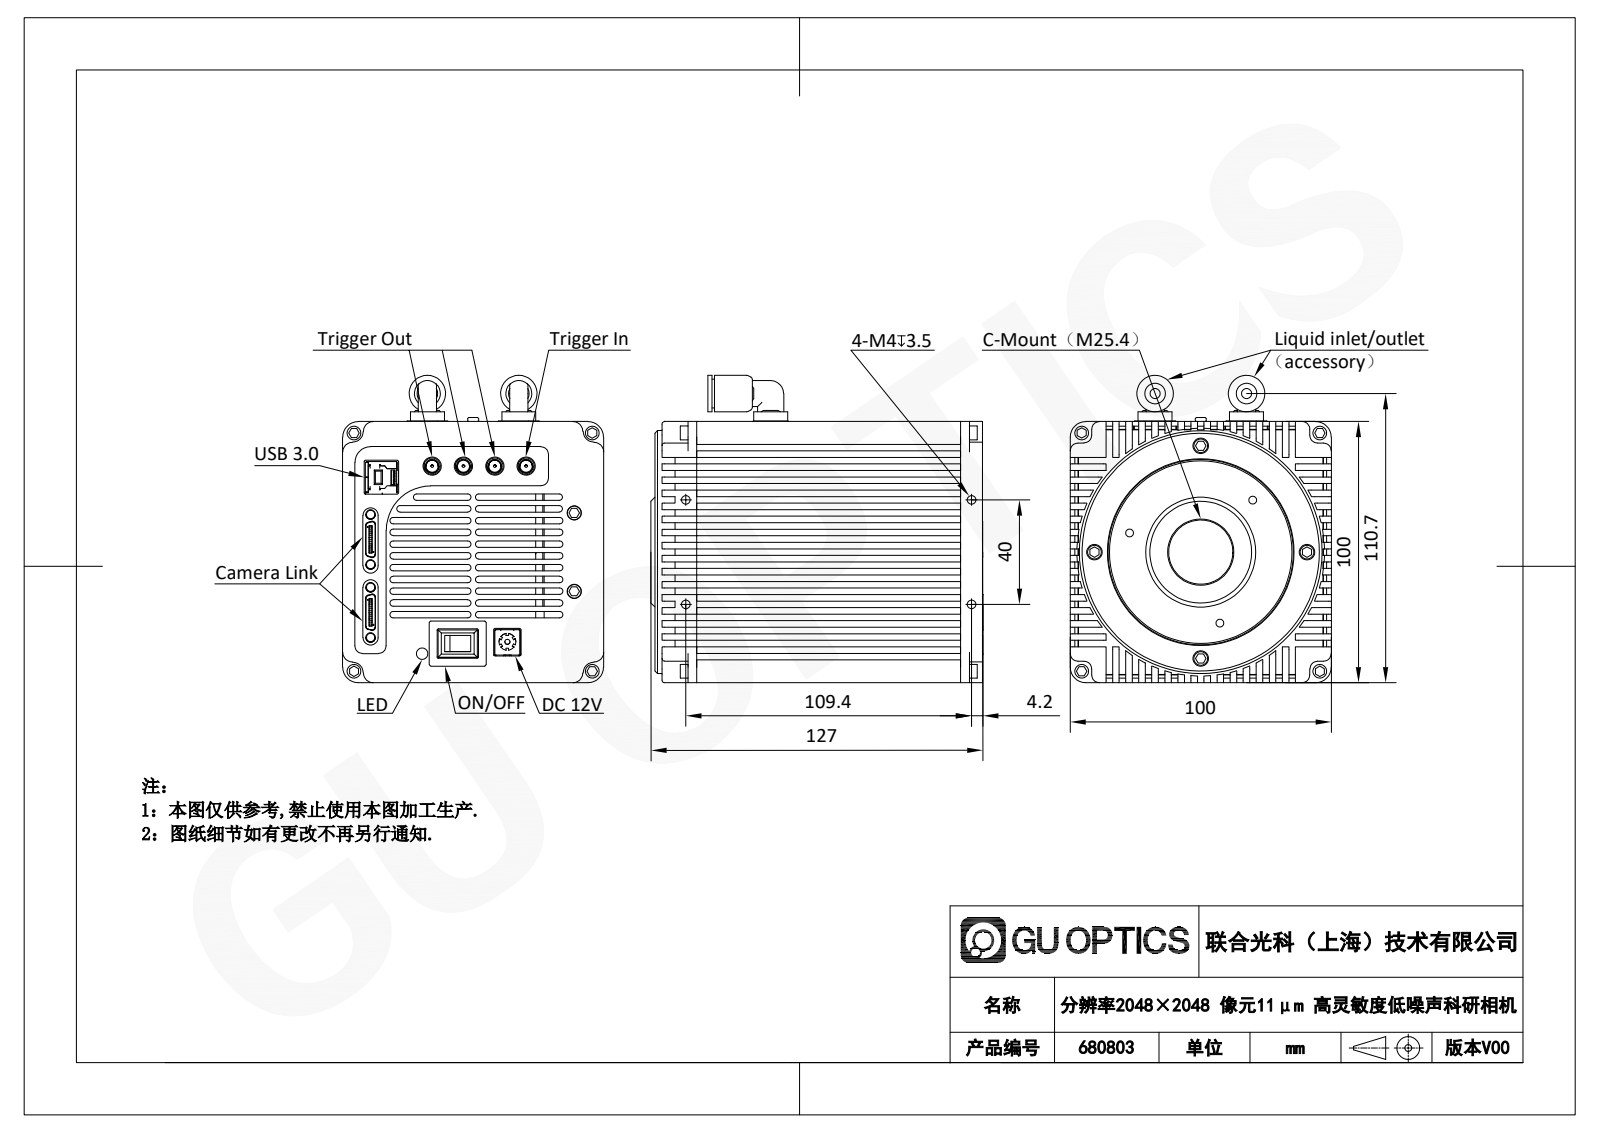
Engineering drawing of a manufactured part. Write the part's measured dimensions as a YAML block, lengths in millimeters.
part_name: "68080358.stp; 68080343.stp; 68080348.stp; 68080337.stp (+8 more)"
step_written_by: "SolidWorks 2024 (CONFIG_CONTROL_DESIGN)"
units: millimeters
bodies: {solids: 64, faces: 5520, planar: 3348, cylindrical: 1705, other: 467}
overall_size: [177.38, 117.7, 100]
volume: 1003000
surface_area: 252717
round_holes:
  - {diameter: 3.2, count: 18}
  - {diameter: 6, count: 12}
  - {diameter: 2.2, count: 10}
  - {diameter: 2.6, count: 10}
  - {diameter: 1.6, count: 6}
  - {diameter: 2, count: 5}
  - {diameter: 1, count: 4}
  - {diameter: 2.5, count: 4}
  - {diameter: 3.4, count: 4}
  - {diameter: 4.3, count: 4}
  - {diameter: 4.65, count: 4}
  - {diameter: 7, count: 4}
round_bosses_or_shafts:
  - {diameter: 0.46, count: 115}
  - {diameter: 3, count: 18}
  - {diameter: 5.3, count: 14}
  - {diameter: 10, count: 6}
  - {diameter: 6, count: 4}
  - {diameter: 4, count: 4}
  - {diameter: 3.8, count: 4}
  - {diameter: 1.6, count: 4}
partial_cylinders:
  - {radius: 1.25, count: 160}
  - {radius: 0.2, count: 90}
  - {radius: 1, count: 69}
  - {radius: 0.25, count: 34}
  - {radius: 0.5, count: 34}
  - {radius: 2.5, count: 32}
  - {radius: 0.3, count: 29}
  - {radius: 2, count: 22}
face_to_face_distances: [1.8, 98.2, 100, 8.4, 117.04, 3, 2.5, 97, 5, 90]
hole_center_spacings: [22.25, 29.51, 42.72, 46.78, 24.96, 26.63, 27, 28.04]
